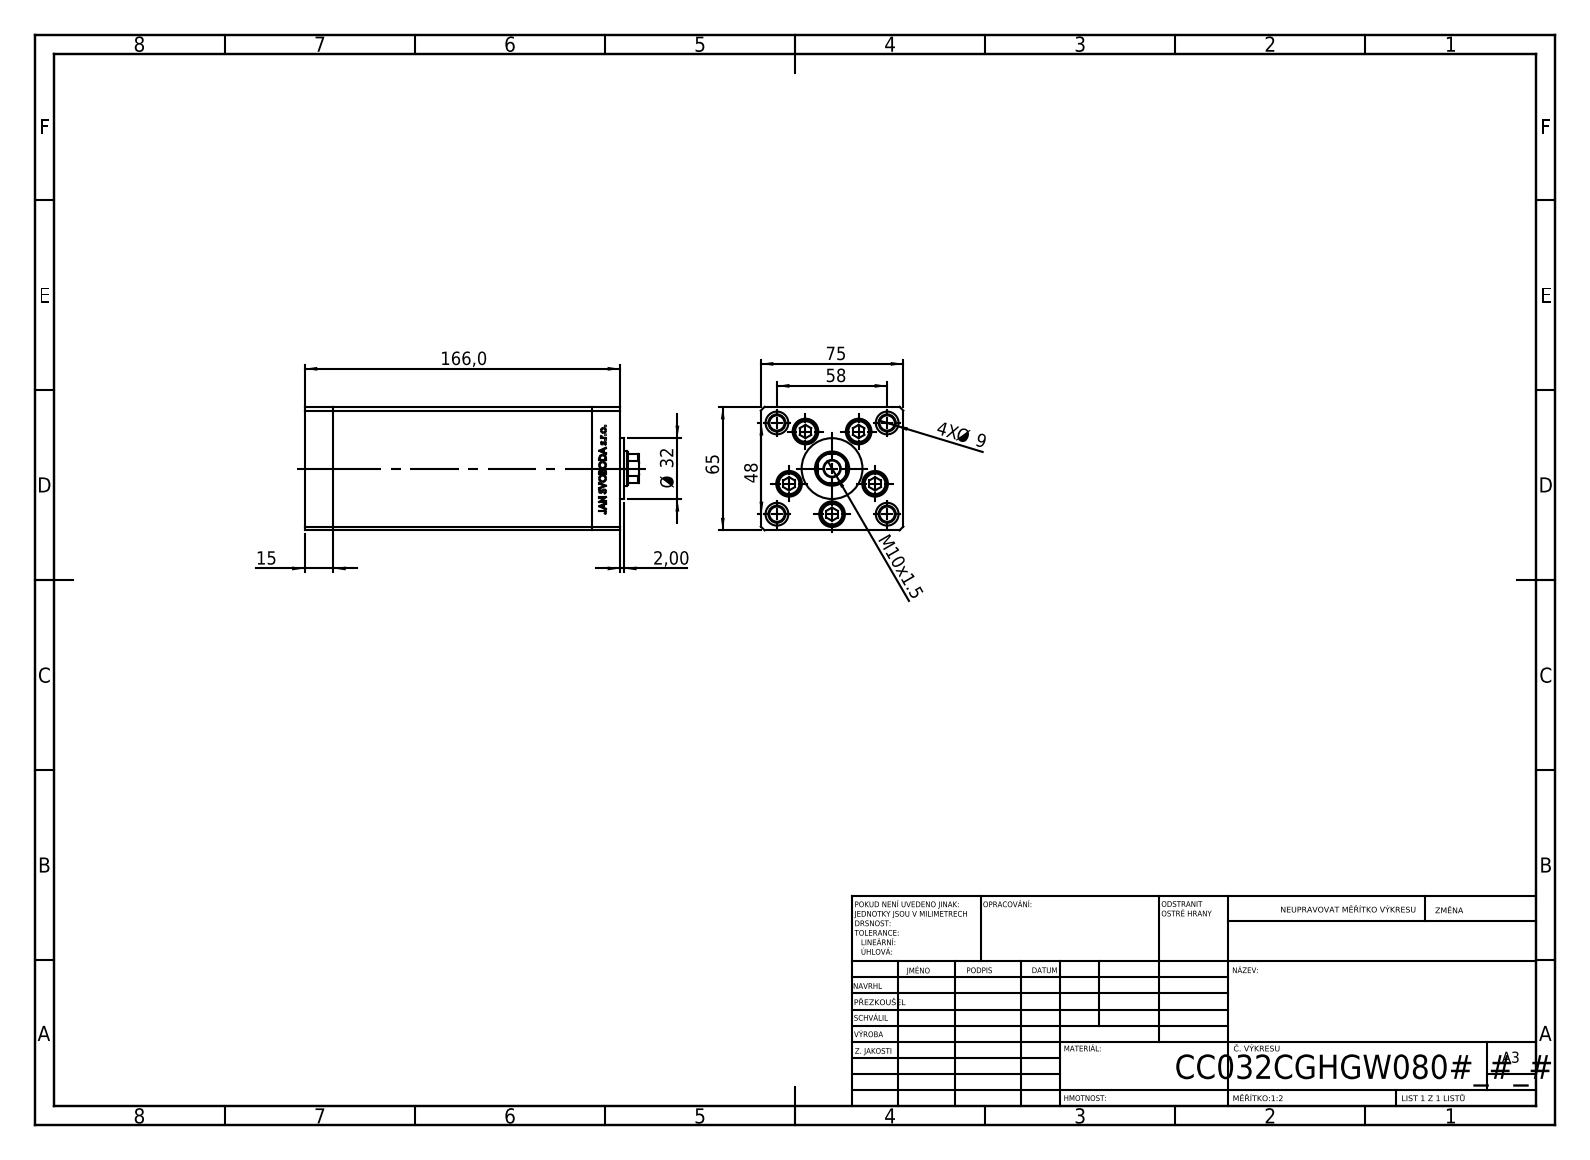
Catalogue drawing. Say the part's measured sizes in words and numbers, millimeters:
The part is named "V220C_C MIDDLE; V220C_VC_C; V220C FRONT; ALLEN BOLT (+1 more)". Its 3-D file was written by "SolidWorks 2019 (CONFIG_CONTROL_DESIGN)". It is 13 solids with 1179 faces: 542 planar, 175 cylindrical and 462 other. Overall it measures 176 by 75 by 65 millimeters. Its volume is 676 888 cubic millimeters and its surface area 143 721 square millimeters. Round holes: 9 of diameter 9, 5 of diameter 13.5, 4 of diameter 2, 4 of diameter 8, 4 of diameter 12, 4 of diameter 13.16, 1 of diameter 8.5, 1 of diameter 12.5, 1 of diameter 18. Round bosses or shafts: 5 of diameter 8, 4 of diameter 12.5, 1 of diameter 32. Partial cylindrical surfaces (rounded edges, fillets, slot ends): 2 of radius 0.93, 1 of radius 8.5. The main face-to-face distances are 75, 65, 15, 136, 151, 166, 28, 13, 142, 9. The hole center spacings are 24, 37.64, 15.67, 17.22, 27.71, 28.83, 29, 32.63.
